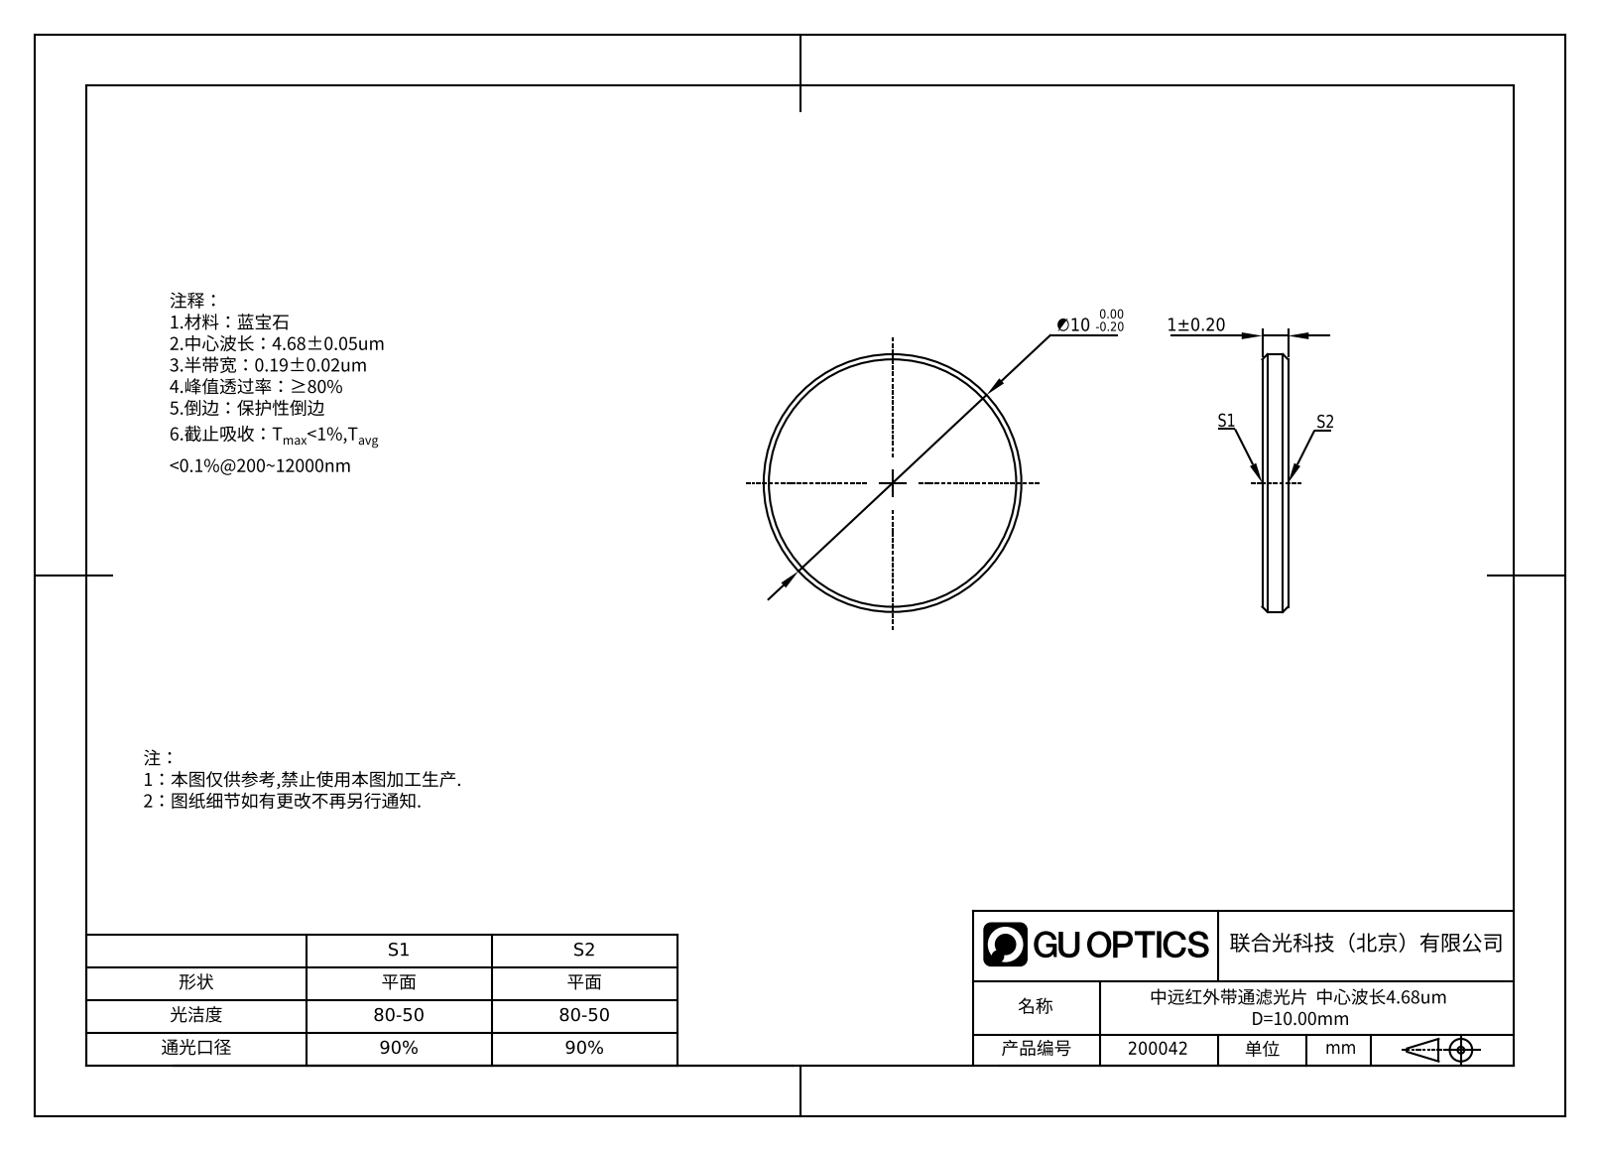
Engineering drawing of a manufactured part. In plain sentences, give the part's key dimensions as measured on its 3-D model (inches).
The part is named "GNIF-190-4680-D10". Its 3-D file was written by "SolidWorks 2022 (AUTOMOTIVE_DESIGN)". It is 1 solid with 8 faces: 2 planar, 2 cylindrical and 4 other. Overall it measures 0.394 by 0.394 by 0.039 inches. Its volume is 0.005 cubic inches and its surface area 0.281 square inches. Round bosses or shafts: 1 of diameter 0.394. The main face-to-face distances are 0.039.
